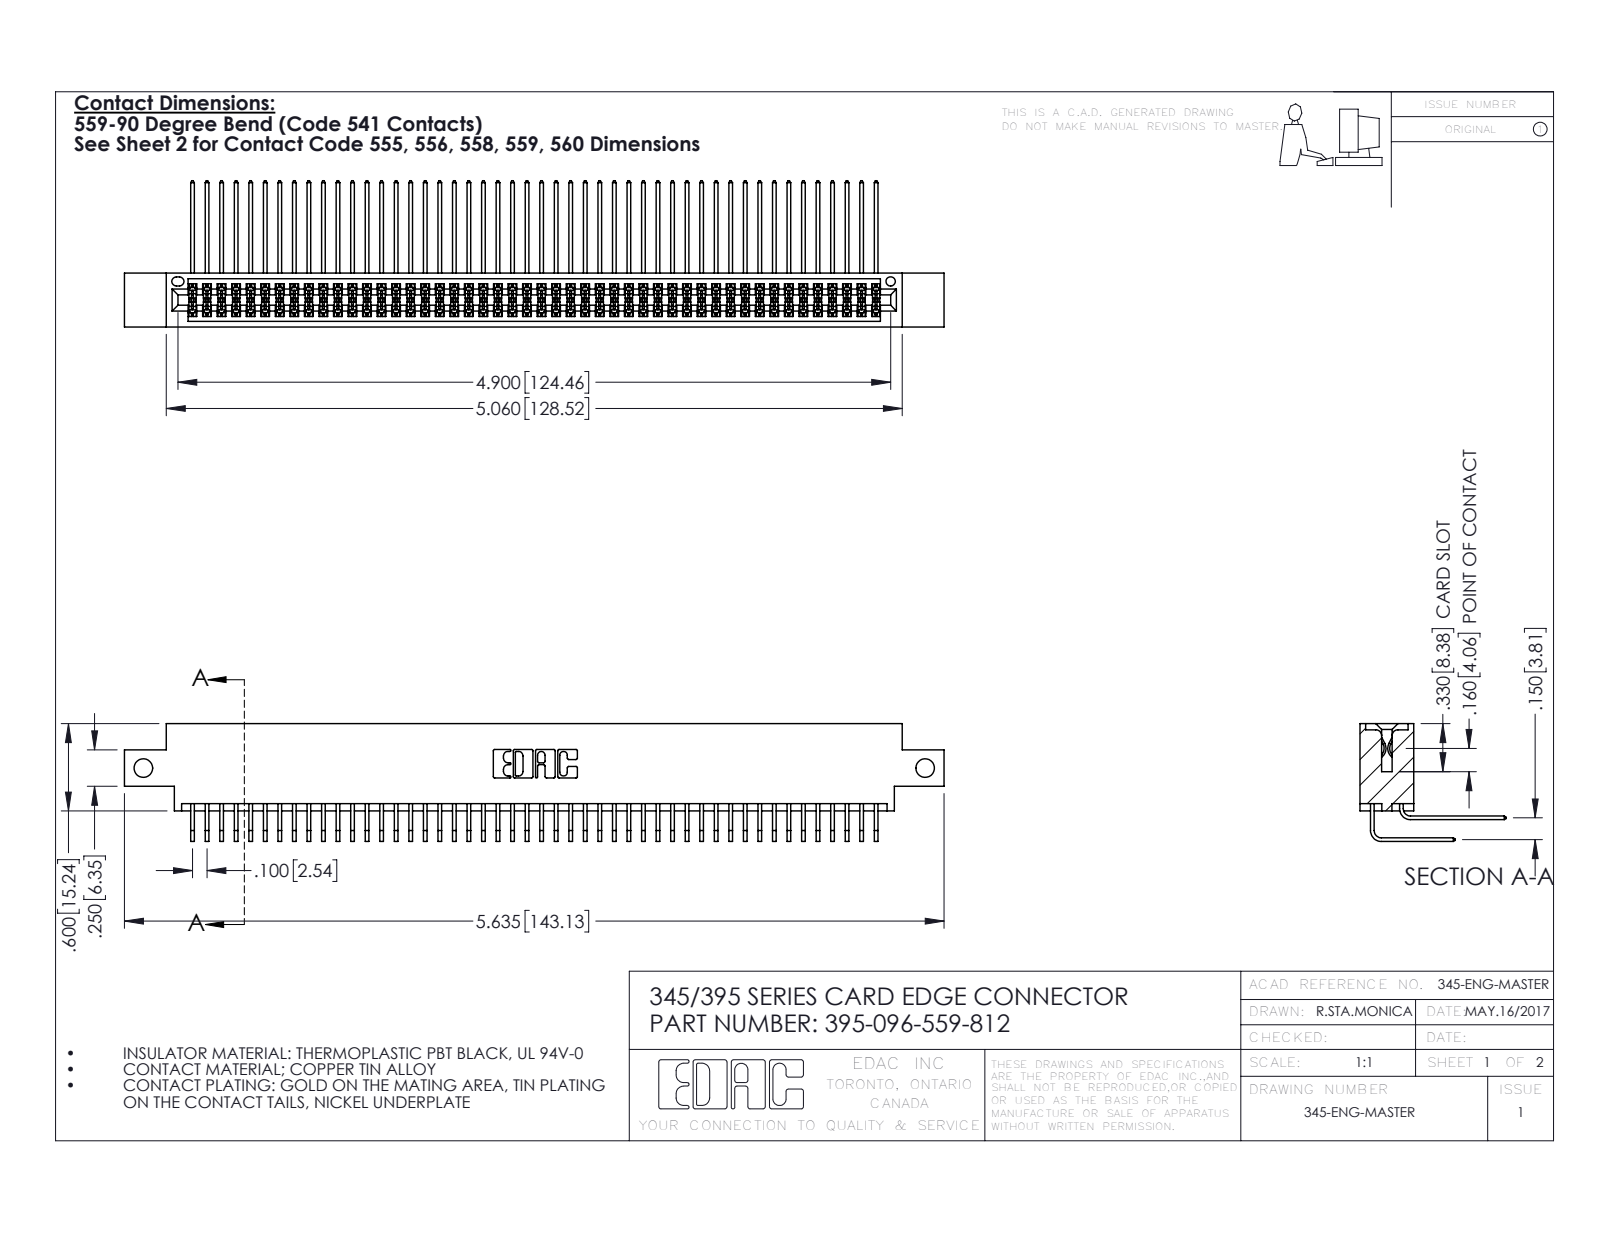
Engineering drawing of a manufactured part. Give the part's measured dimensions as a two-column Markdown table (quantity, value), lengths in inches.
| quantity | value |
| --- | --- |
| part name | 395-096-559-812; 345 Part_0.170 Offset - Side Mount; 345-292-001_559 Tail - 2; 345-292-001_558 559 Tail - 1 |
| STEP written by | SolidWorks 2016 (CONFIG_CONTROL_DESIGN) |
| units | inches |
| bodies | 97 solids, 5122 faces (3444 planar, 1678 cylindrical, 0 other) |
| overall size | 5.635 × 1.005 × 0.809 |
| volume | 0.873 in³ |
| surface area | 37.02 in² |
| round holes (diameter × count) | 0.128 × 2, 0.064 × 1 |
| partial cylindrical surfaces (radius × count) | 0.006 × 145, 0.01 × 22, 0.007 × 6, 0.031 × 6, 0.026 × 3, 0.014 × 2, 0.019 × 2, 0.022 × 2 |
| main face-to-face distances | 0.072, 0.298, 0.37, 0.2, 0.098, 0.272, 0.025, 0.225, 0.175, 0.15 |
| hole center spacings | 5.375 |
